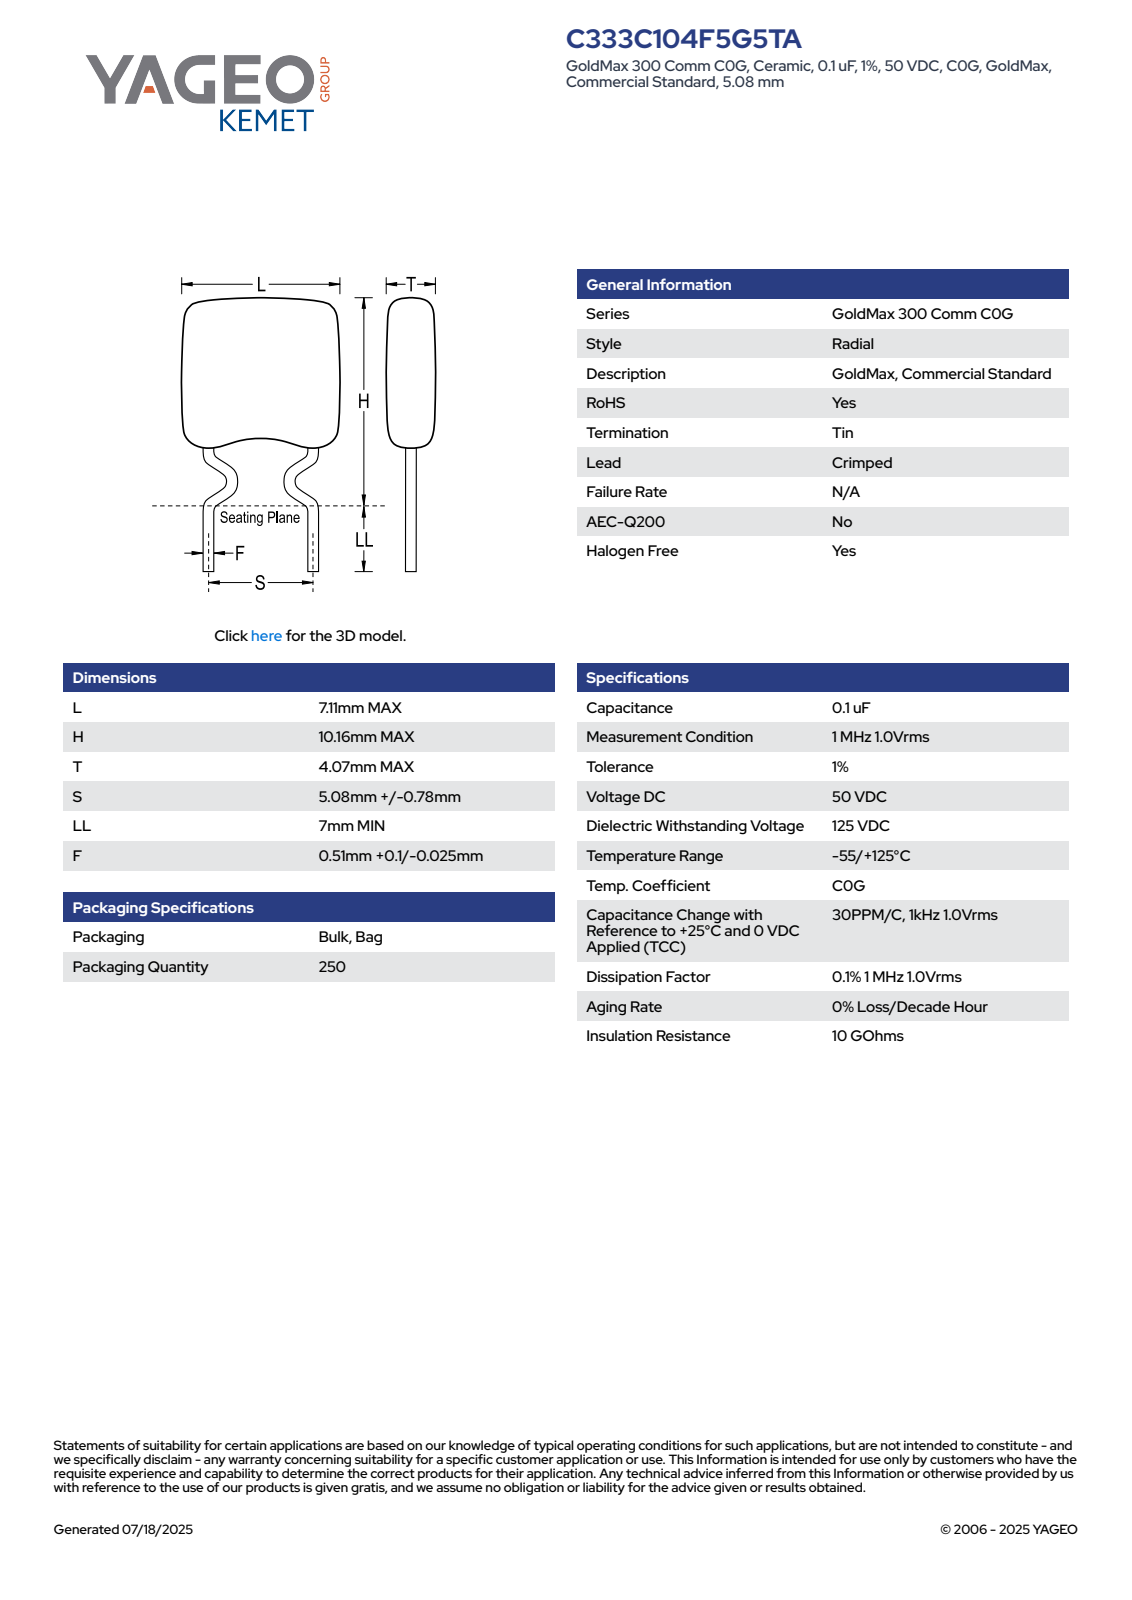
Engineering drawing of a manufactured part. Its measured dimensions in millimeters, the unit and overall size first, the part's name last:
Units: millimetres
Overall size (bounding box): 17.16 × 7.11 × 4.08
Round bosses / shafts (diameter × count): ⌀0.61 ×2
Partial cylindrical surfaces — rounded edges, fillets, slot ends (radius × count): R1 ×12
Main face-to-face distances: 4.07, 7.11, 6.73, 4.08, 2.88, 3.85, 0.97, 0.42, 1.09, 3.96
Volume: 184 mm³ · Surface area: 228 mm²
Bodies: 4 solids, 112 faces (66 planar, 18 cylindrical, 28 other)
Part name (STEP PRODUCT): CCRC333_L7.11H10.16T4.07S5.08LL7F0.61
STEP written by: SolidWorks 2014 (AUTOMOTIVE_DESIGN)
